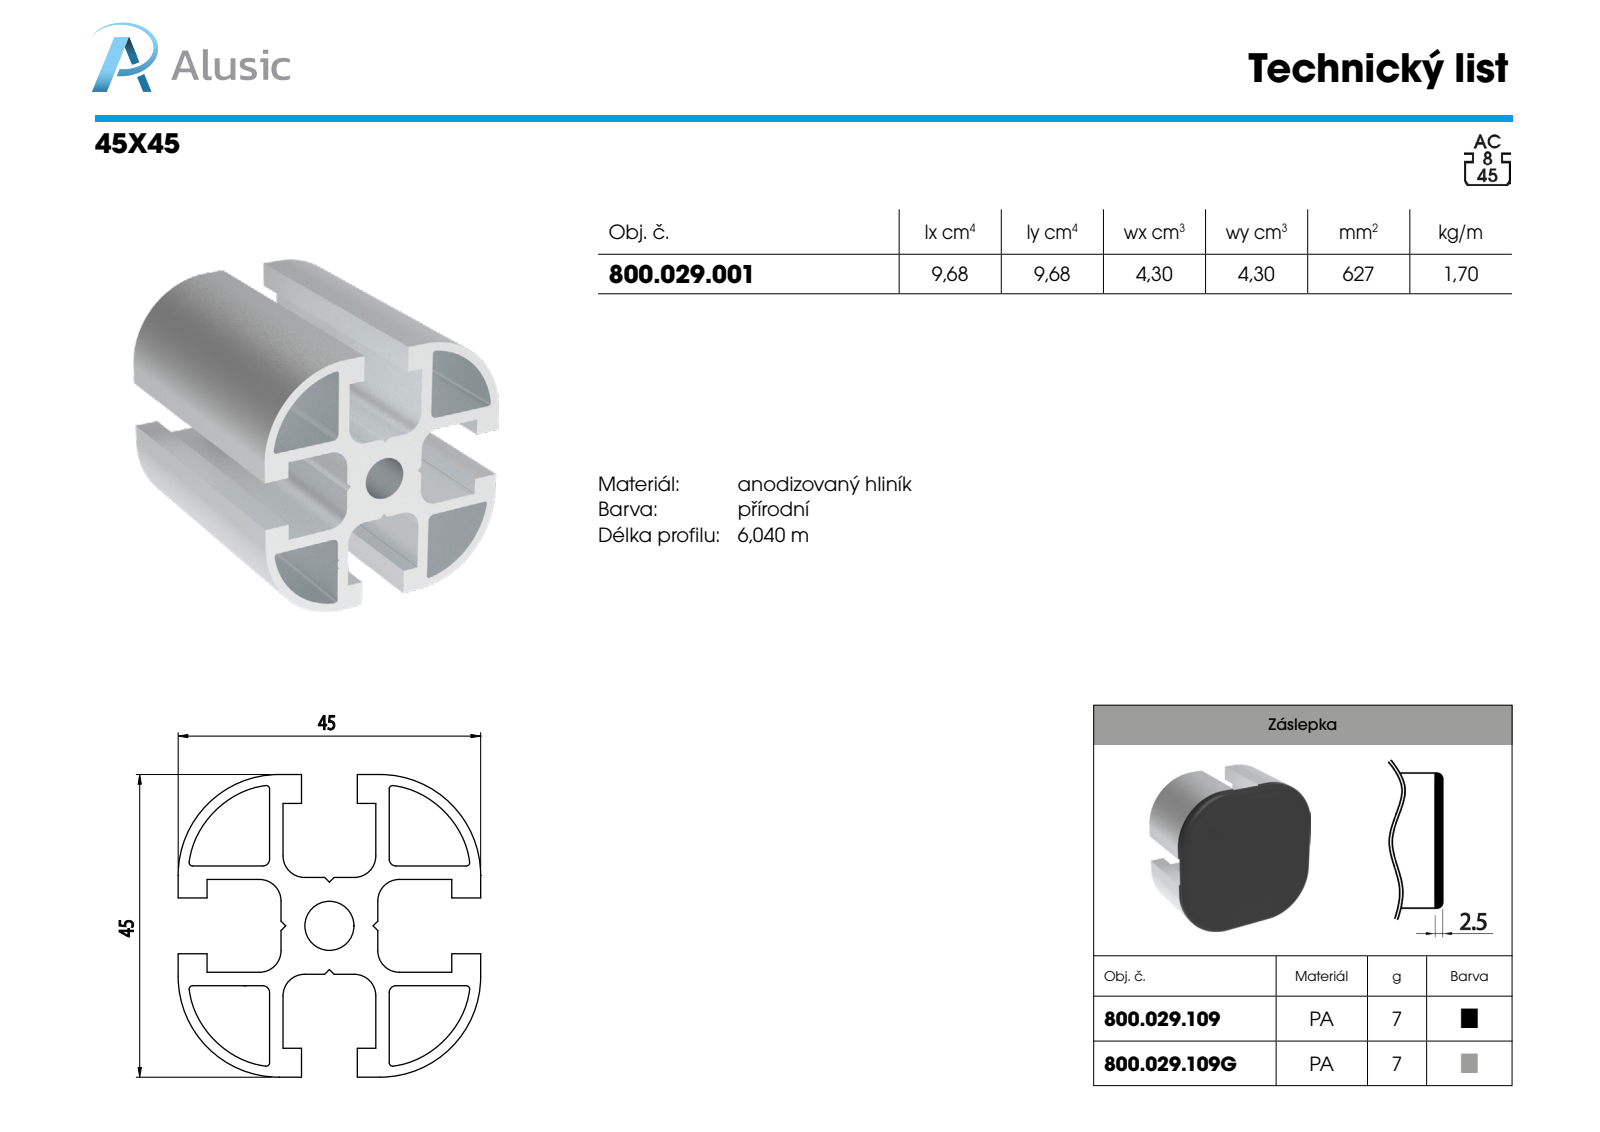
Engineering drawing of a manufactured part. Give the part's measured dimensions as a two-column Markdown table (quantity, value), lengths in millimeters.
| quantity | value |
| --- | --- |
| part name | 800.029.001 |
| STEP written by | SolidWorks 2018 (AUTOMOTIVE_DESIGN) |
| units | millimeters |
| bodies | 1 solid, 96 faces (62 planar, 34 cylindrical, 0 other) |
| overall size | 100 × 45 × 45 |
| volume | 62 744 mm³ |
| surface area | 51 369 mm² |
| round holes (diameter × count) | 7.3 × 1 |
| partial cylindrical surfaces (radius × count) | 0.5 × 8, 3.2 × 8, 1 × 4, 13.5 × 4, 15 × 4, 0.2 × 1 |
| main face-to-face distances | 15.8, 2, 17.8, 4.75, 2.75, 13.05, 11.05, 13.8, 13.6, 15.6 |
